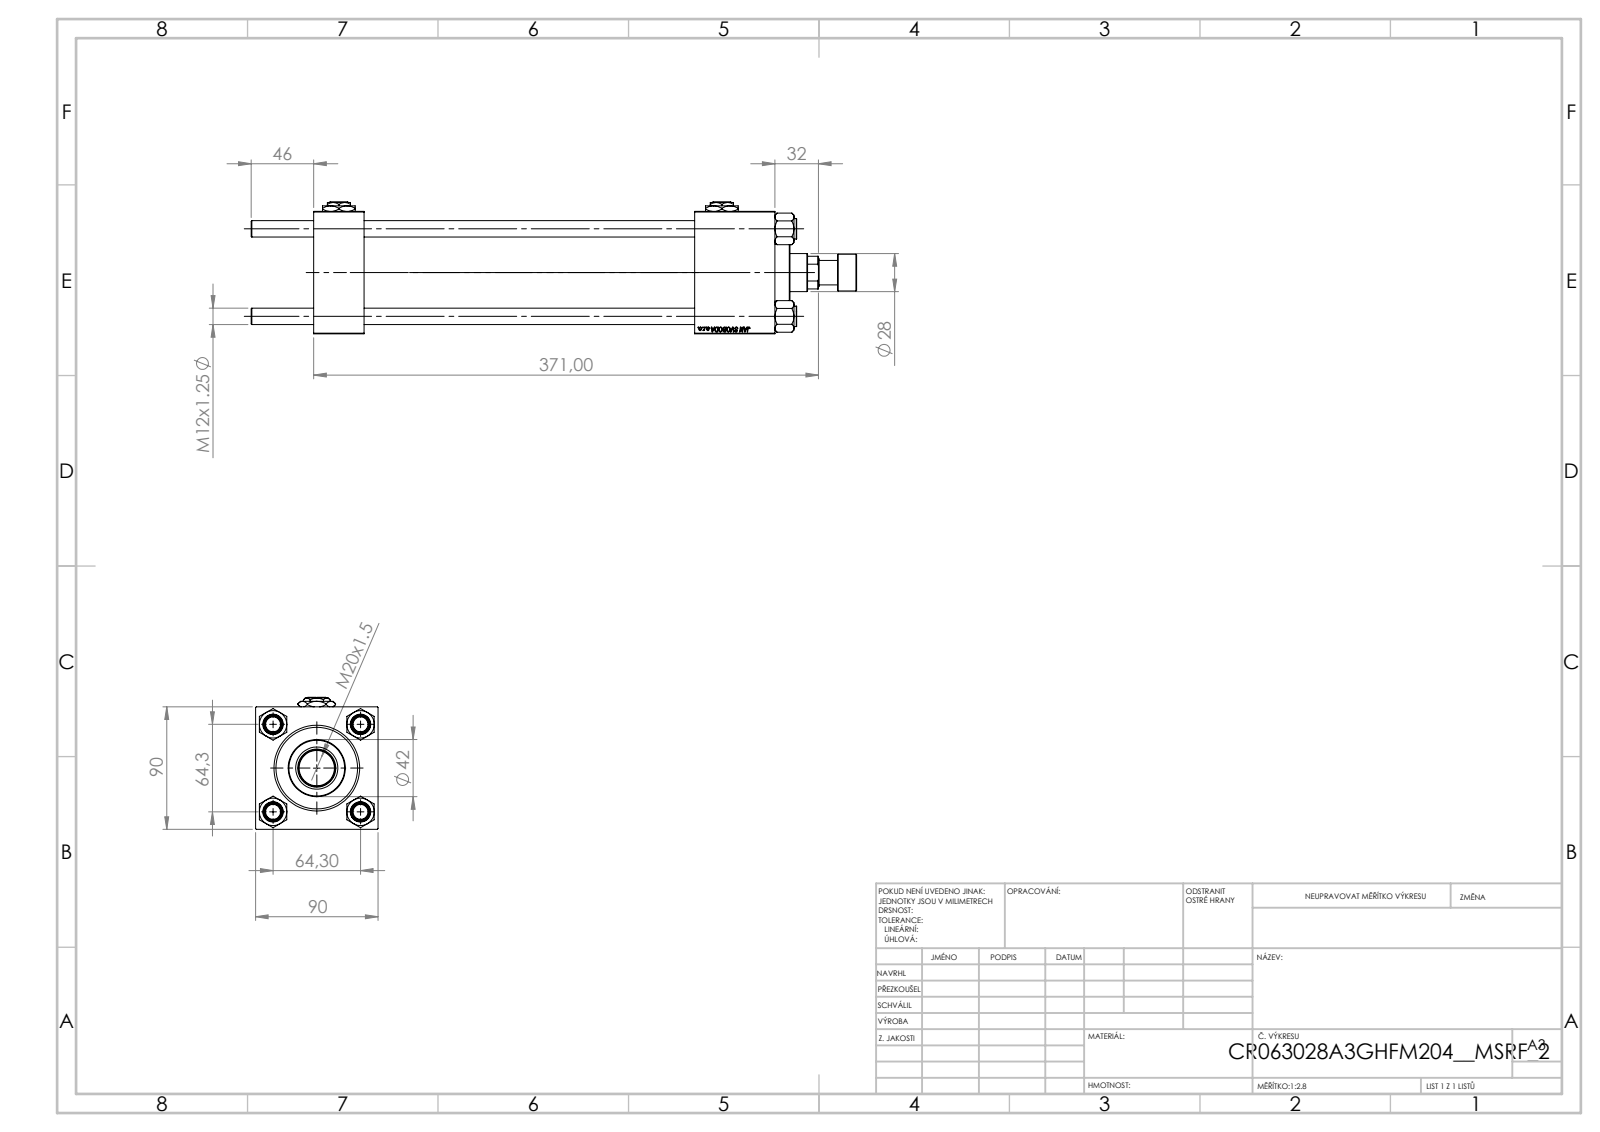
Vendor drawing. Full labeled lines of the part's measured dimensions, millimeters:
Part name (STEP PRODUCT): NUT_M5; V215_VC_A; CR025_012_A_0_G_A_G_M_020_+#_##_TYCINKA; V215CR_VCP (+3 more)
STEP written by: SolidWorks 2019 (CONFIG_CONTROL_DESIGN)
Units: millimetres
Bodies: 13 solids, 307 faces (107 planar, 46 cylindrical, 154 other)
Overall size (bounding box): 445 × 95.77 × 84.43
Volume: 576 510 mm³ · Surface area: 132 400 mm²
Round holes (diameter × count): ⌀12 ×4, ⌀18.5 ×1, ⌀28 ×1, ⌀31 ×1
Round bosses / shafts (diameter × count): ⌀15 ×4, ⌀63 ×1, ⌀60 ×1, ⌀42 ×1, ⌀27 ×1, ⌀18 ×1
Main face-to-face distances: 39, 273.3, 234.3, 302, 263, 28.7, 20.13, 32.15, 55.68, 14
Hole centre spacings: 45.47, 64.3, 90.93
